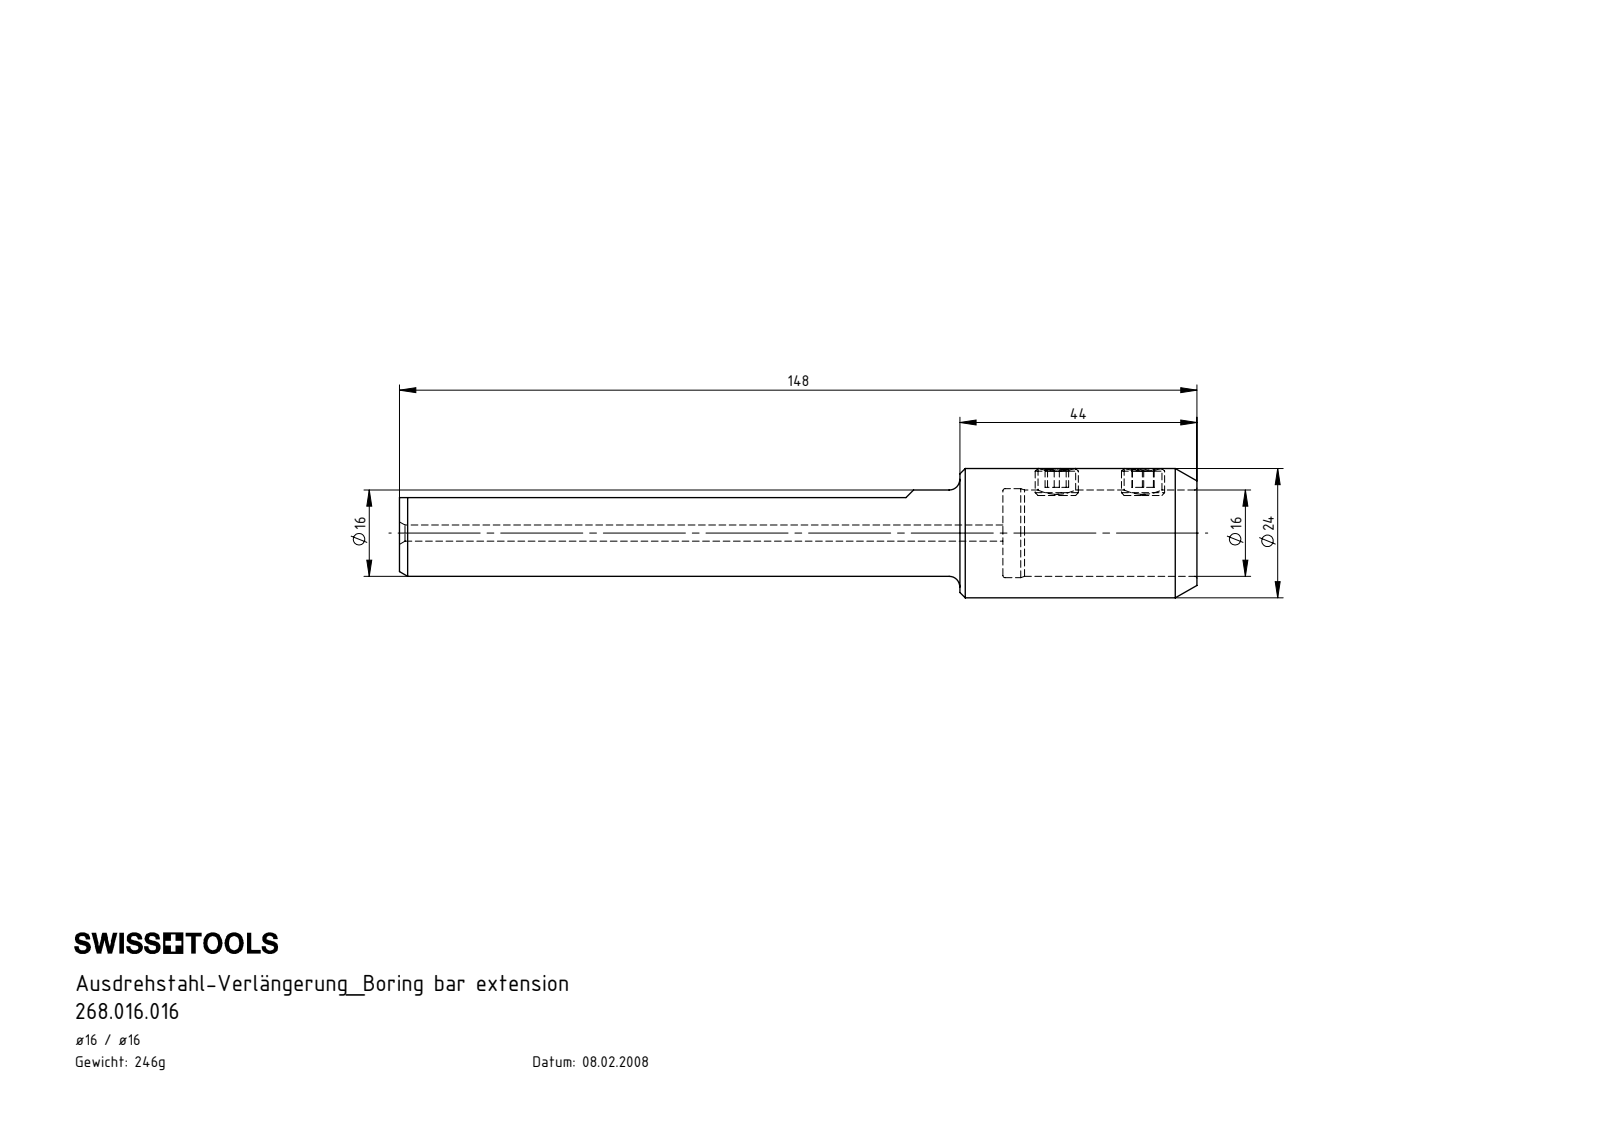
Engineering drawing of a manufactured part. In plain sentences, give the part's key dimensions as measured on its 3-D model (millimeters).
The part is named "U16-U16.K01.148_A; U16-U16.K01.148; U16-ER1.001.005_A". Its 3-D file was written by "SolidWorks 2017 (CONFIG_CONTROL_DESIGN)". It is 3 solids with 89 faces: 34 planar, 22 cylindrical and 33 other. Overall it measures 148 by 24 by 24 millimeters. Its volume is 30 231 cubic millimeters and its surface area 13 212 square millimeters. Round holes: 2 of diameter 4, 2 of diameter 7, 1 of diameter 5, 1 of diameter 16, 1 of diameter 16.5. Round bosses or shafts: 2 of diameter 8, 1 of diameter 24. The main face-to-face distances are 112, 0.4, 148, 36, 104, 8, 44, 5.4, 5, 4. The hole center spacings are 16.
